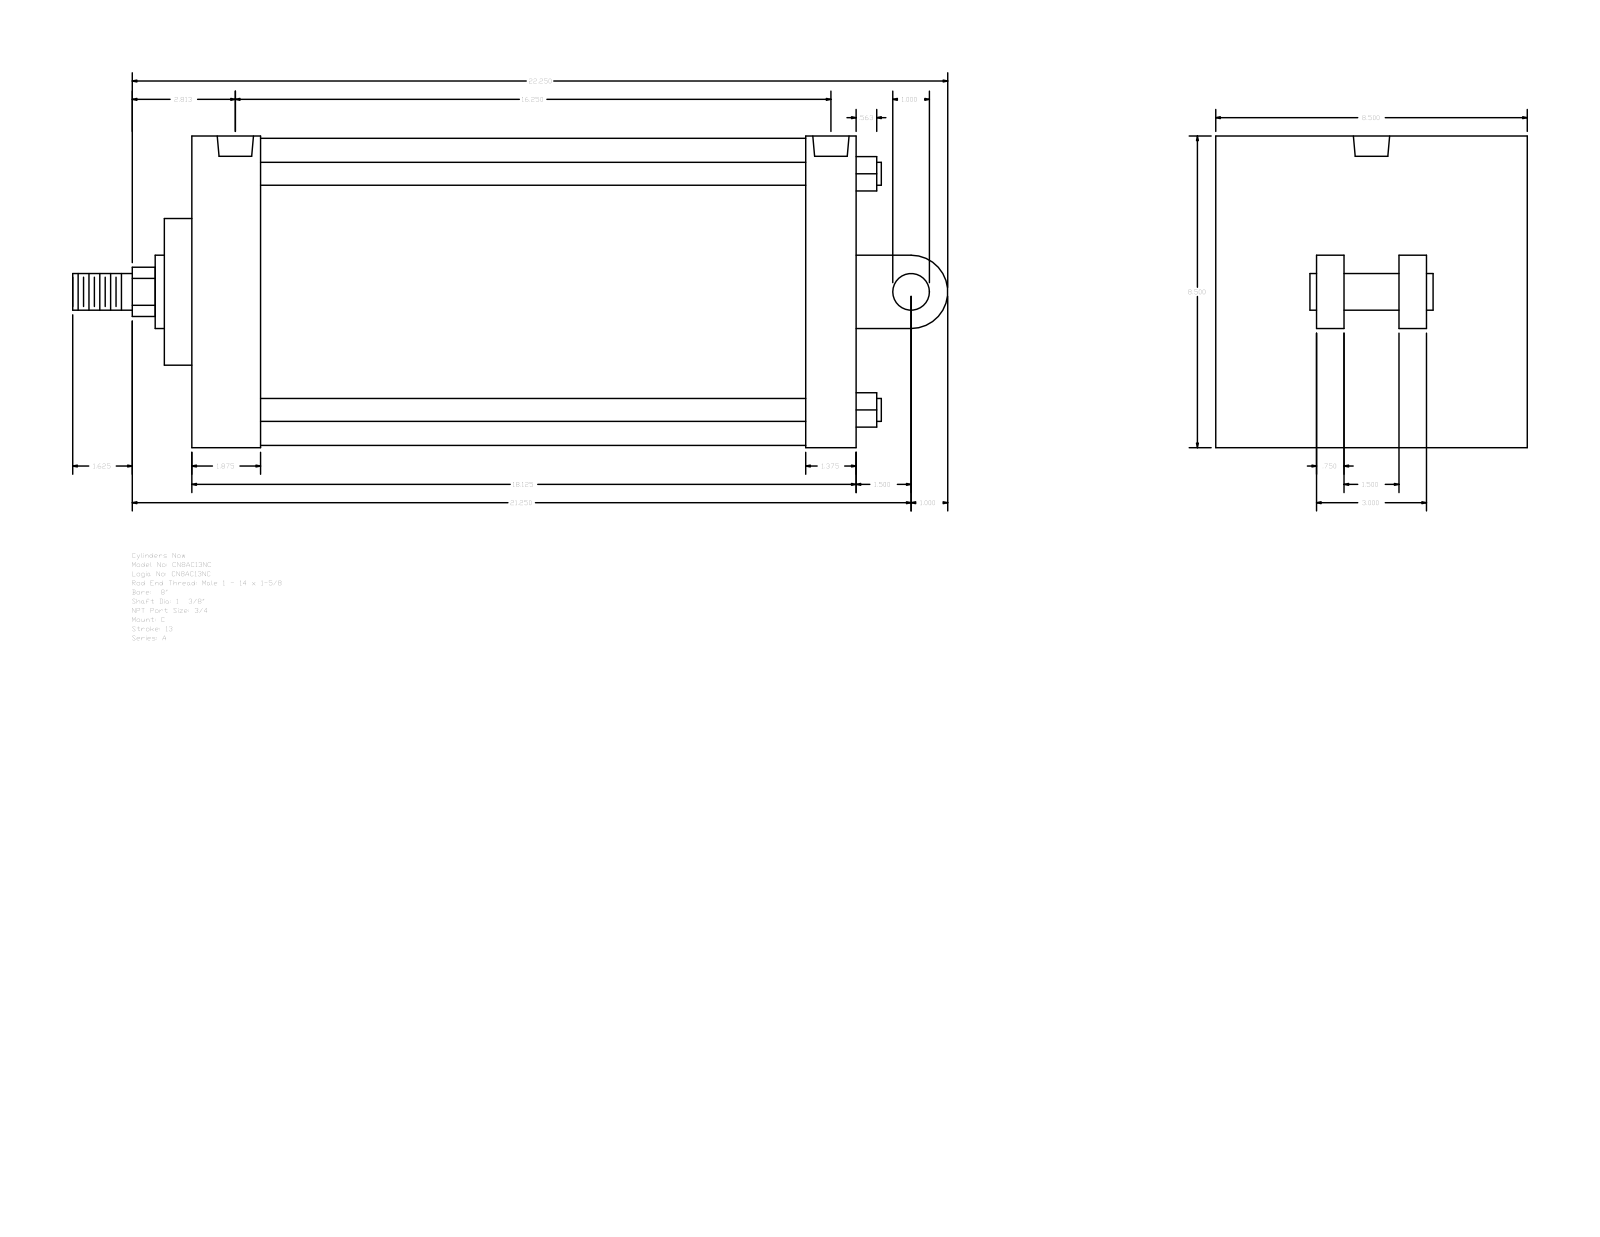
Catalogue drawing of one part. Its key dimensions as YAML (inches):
part_name: "A_C__0800_1.375"
step_written_by: "GSSL Pune (CONFIG_CONTROL_DESIGN)"
units: inches
bodies: {solids: 0, faces: 104, planar: 75, cylindrical: 29, other: 0}
overall_size: [23.875, 8.5, 8.5]
round_holes:
  - {diameter: 0.594, count: 4}
  - {diameter: 0.989, count: 2}
round_bosses_or_shafts:
  - {diameter: 0.625, count: 4}
  - {diameter: 1, count: 2}
  - {diameter: 8.375, count: 1}
  - {diameter: 2, count: 1}
  - {diameter: 1.375, count: 1}
partial_cylinders:
  - {radius: 0.672, count: 1}
  - {radius: 1, count: 1}
face_to_face_distances: [18.125, 8.5, 2.25, 1.875, 16.25, 16.75, 14.875, 1.375, 3.5, 2.75]
hole_center_spacings: [0.25, 15.75, 16, 16.25]
